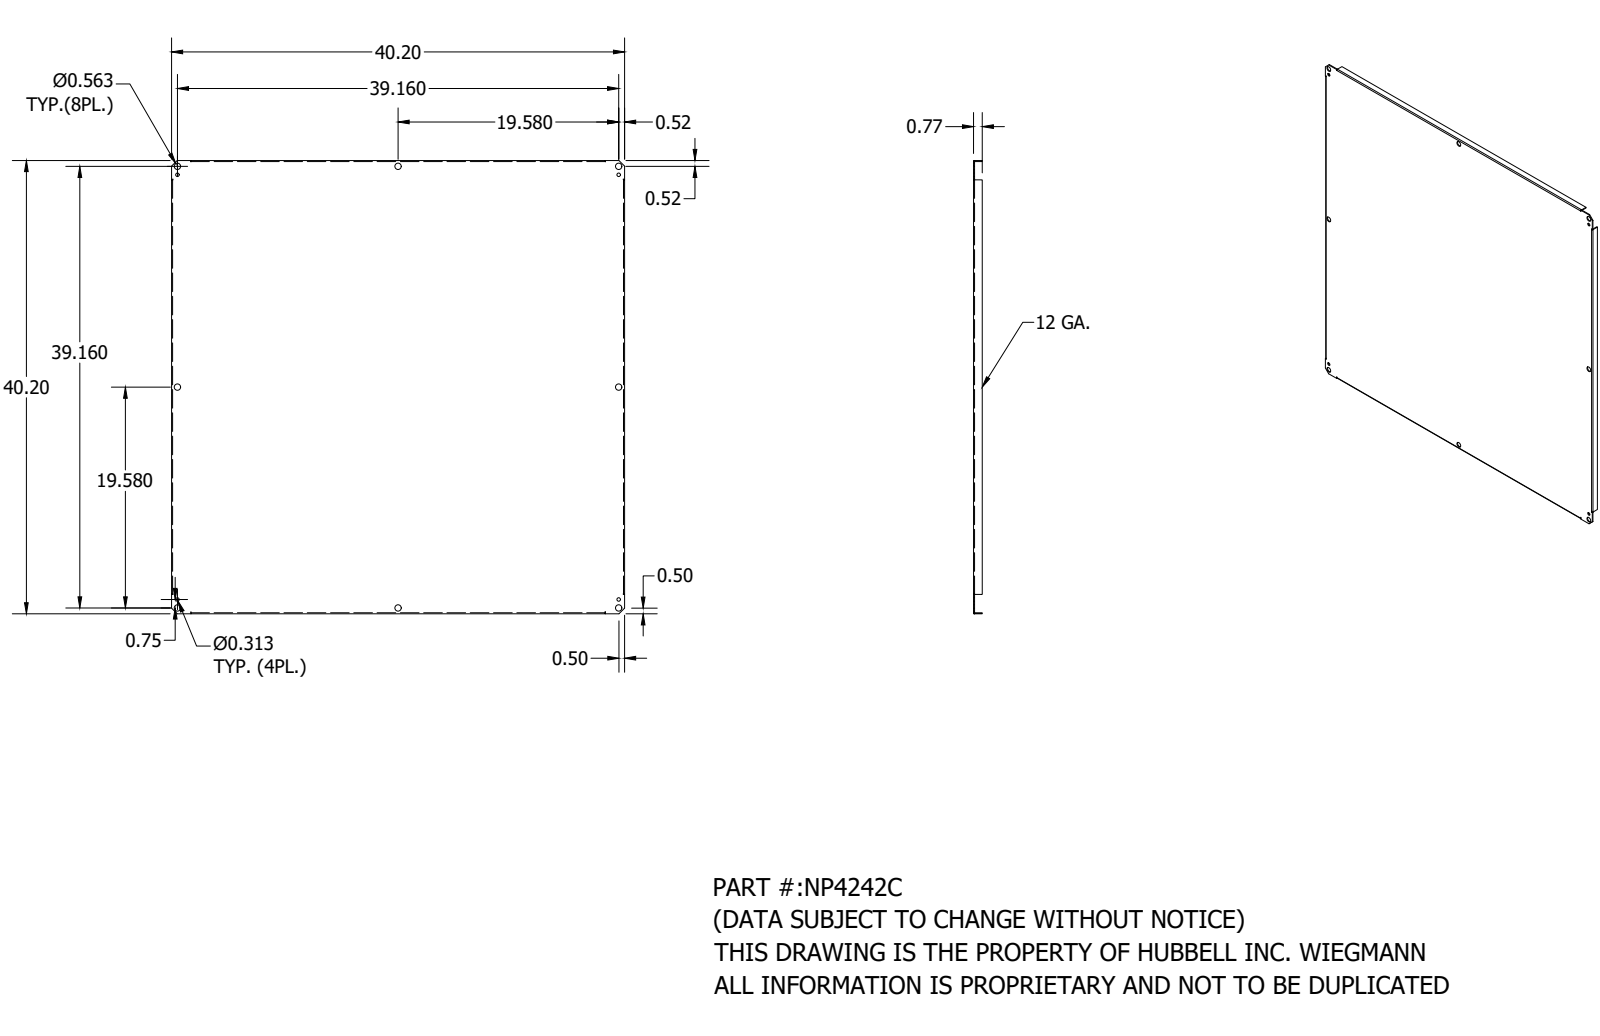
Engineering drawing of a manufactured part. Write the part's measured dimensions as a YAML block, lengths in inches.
part_name: "NP4242C"
step_written_by: "Autodesk Inventor 2018 (AUTOMOTIVE_DESIGN)"
units: inches
bodies: {solids: 1, faces: 70, planar: 50, cylindrical: 20, other: 0}
overall_size: [40.2, 40.2, 0.774]
volume: 160.3
surface_area: 3436
round_holes:
  - {diameter: 0.563, count: 8}
  - {diameter: 0.313, count: 4}
partial_cylinders:
  - {radius: 0.016, count: 4}
  - {radius: 0.109, count: 4}
face_to_face_distances: [0.094, 40.106, 40.2, 40.013, 0.68, 0.774, 1.718, 38.482, 1.624, 38.388]
hole_center_spacings: [19.58, 39.16, 43.782, 0.75, 18.83, 19.594, 27.69, 38.41]
